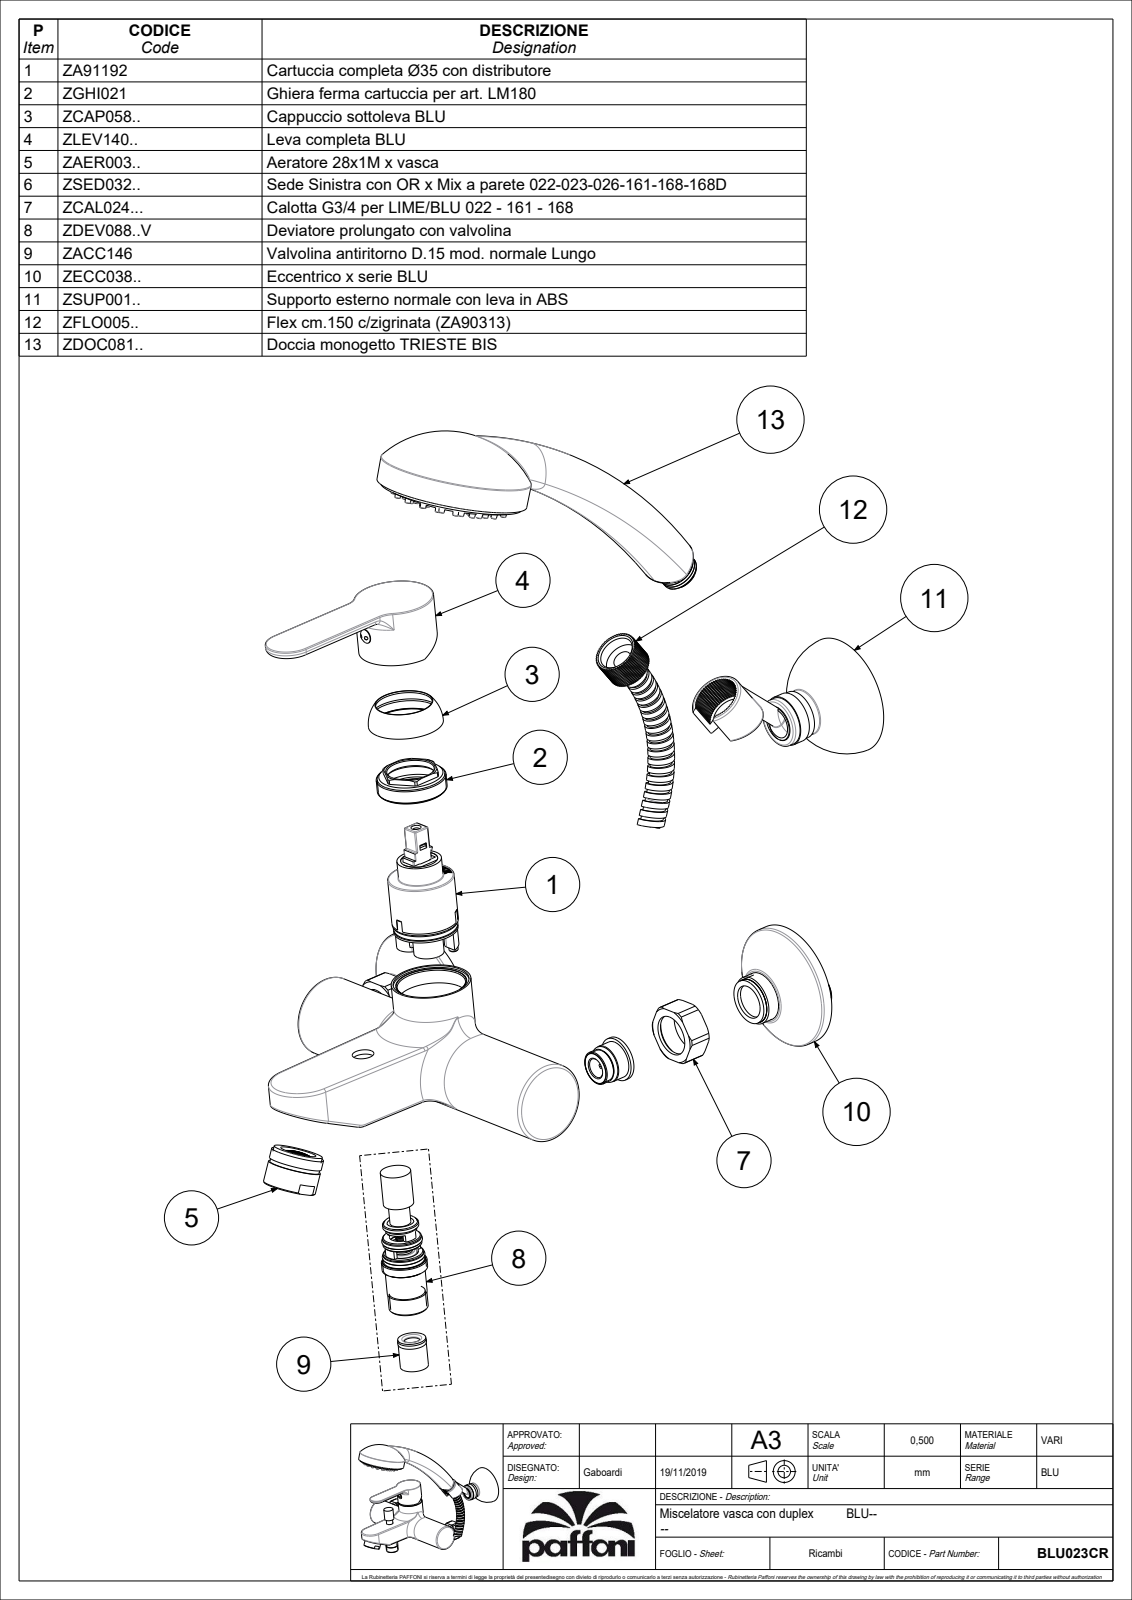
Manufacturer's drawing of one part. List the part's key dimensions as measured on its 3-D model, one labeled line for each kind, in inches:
Part name (STEP PRODUCT): BLU023CR
STEP written by: CREO PARAMETRIC BY PTC INC, 2019030 (CONFIG_CONTROL_DESIGN)
Units: inches
Bodies: 0 solids, 983 faces (364 planar, 384 cylindrical, 235 other)
Overall size (bounding box): 11.673 × 11.644 × 10.42
Round holes (diameter × count): ⌀0.059 ×11, ⌀0.709 ×3, ⌀0.374 ×2, ⌀0.472 ×2, ⌀0.63 ×2, ⌀0.642 ×2, ⌀0.787 ×2, ⌀2.5 ×2, ⌀0.118 ×1, ⌀0.236 ×1, ⌀0.394 ×1, ⌀0.433 ×1
Round bosses / shafts (diameter × count): ⌀0.118 ×48, ⌀2.579 ×2, ⌀1.654 ×2, ⌀1.031 ×2, ⌀0.984 ×2, ⌀0.827 ×2, ⌀0.819 ×2, ⌀0.807 ×2
Partial cylindrical surfaces — rounded edges, fillets, slot ends (radius × count): R0.03 ×21, R0.047 ×8, R0.02 ×6, R0.059 ×6, R0.236 ×4, R0.394 ×4, R0.039 ×3, R0.098 ×2
Main face-to-face distances: 0.079, 2.638, 2.717, 4.37, 7.008, 4.291, 1.654, 0.039, 7.087, 2.028
Hole centre spacings: 0.556, 2.009, 0.394, 5.906, 0.411, 0.632, 0.633, 0.972
